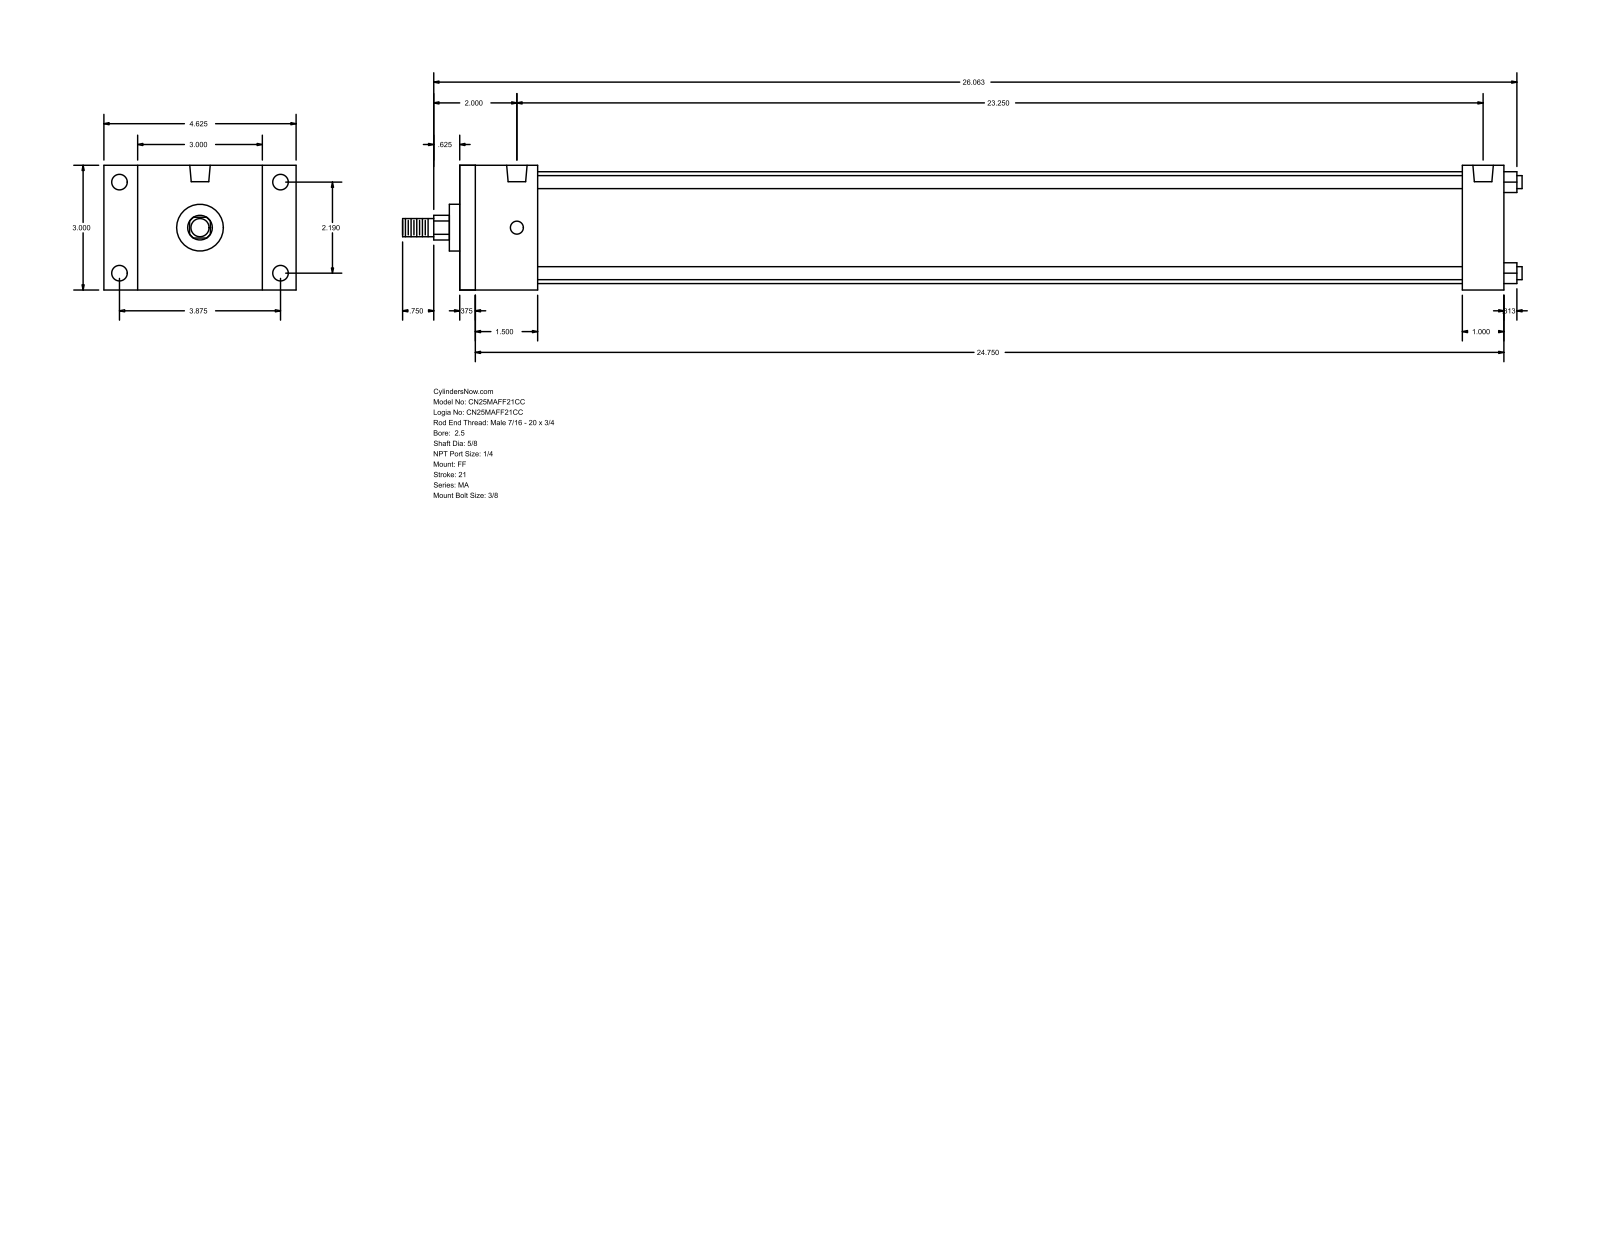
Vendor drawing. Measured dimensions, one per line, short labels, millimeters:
name: MA_FF__0250_0.625
written by: GSSL Pune (CONFIG_CONTROL_DESIGN)
unit: mm
bodies: 0 solids, 92 faces (64 planar, 28 cylindrical, 0 other)
size: 684.21 × 117.47 × 76.2
holes: 4× ⌀7.94, 4× ⌀9.53, 2× ⌀12.49
bosses: 4× ⌀7.94, 1× ⌀68.33, 1× ⌀28.57, 1× ⌀15.88, 1× ⌀11.11
rounds: 1× R7.54
face distances: 76.2, 638.17, 628.65, 9.52, 25.4, 47.62, 612.77, 38.1, 603.25, 565.15
hole spacings: 55.62, 98.42, 113.05, 590.55
